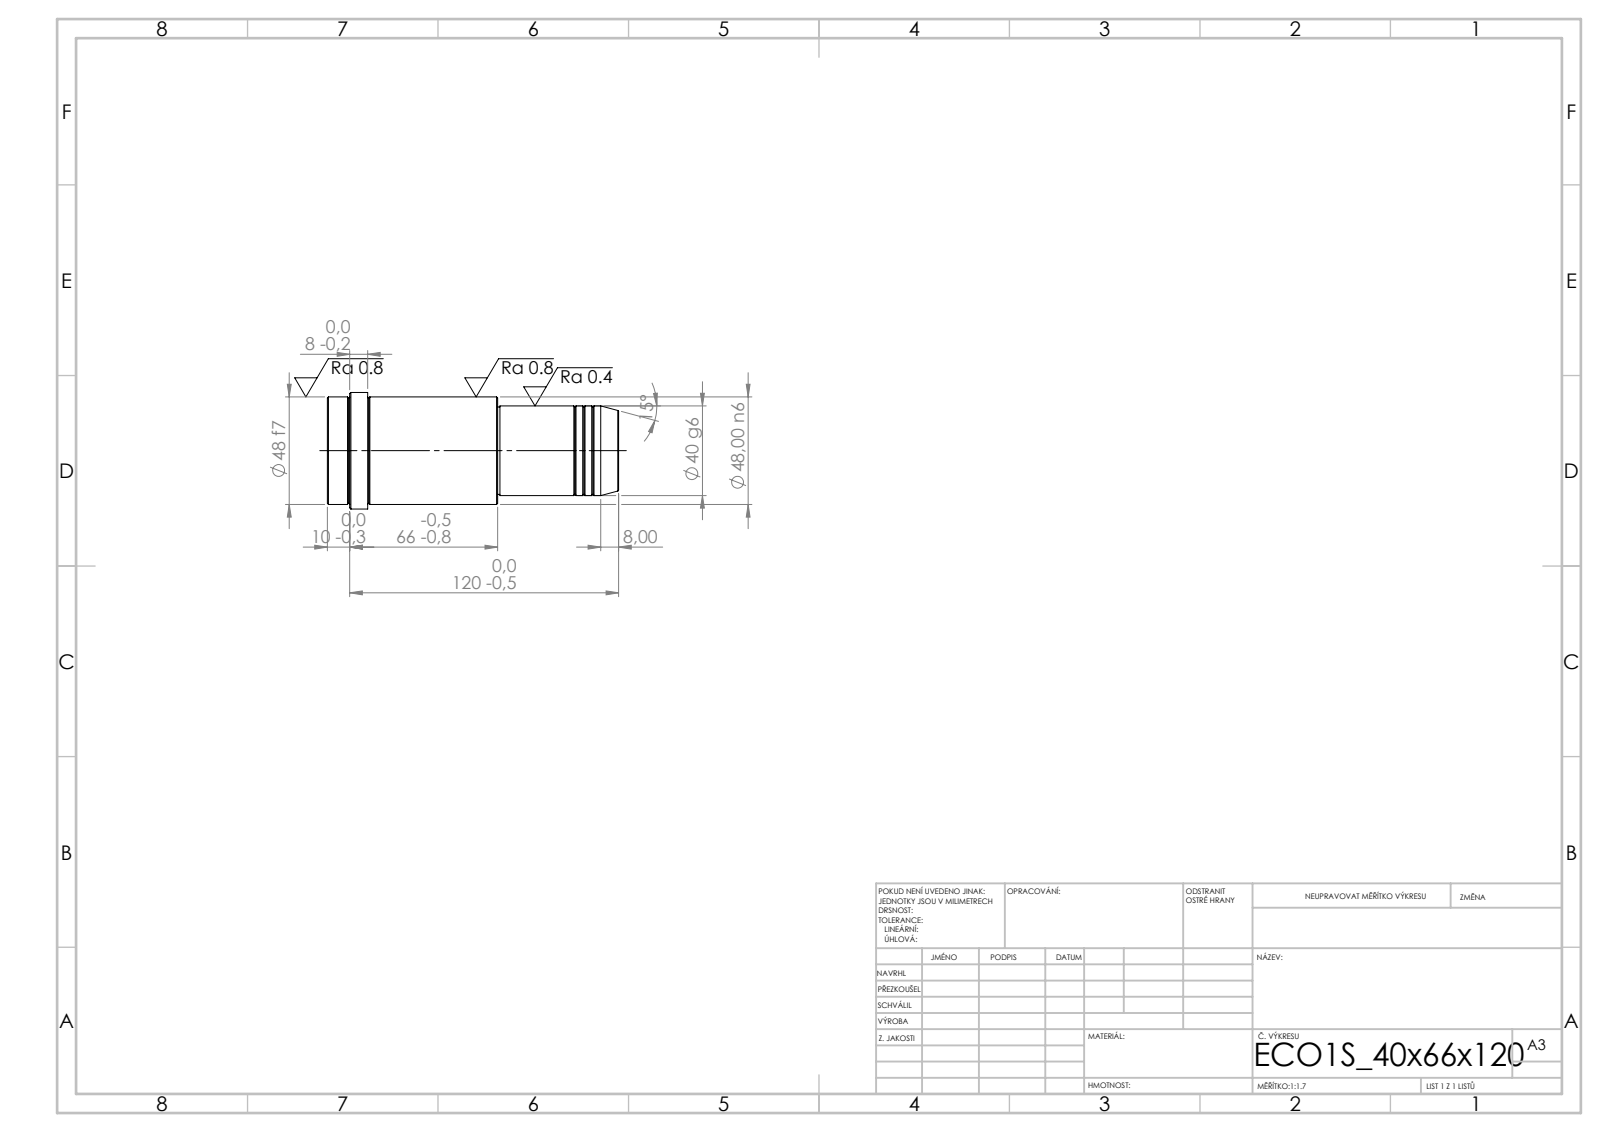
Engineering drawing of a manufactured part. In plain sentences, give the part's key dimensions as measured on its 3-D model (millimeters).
Its 3-D file was written by "SolidWorks 2019 (CONFIG_CONTROL_DESIGN)". It is 1 solid with 52 faces: 6 planar, 16 cylindrical and 30 other. Overall it measures 130 by 52 by 52 millimeters. Its volume is 206 472 cubic millimeters and its surface area 22 662 square millimeters. Round bosses or shafts: 1 of diameter 52, 1 of diameter 48, 1 of diameter 40, 1 of diameter 39. The main face-to-face distances are 130, 54, 76, 112, 58, 18, 120, 66, 8, 10.
